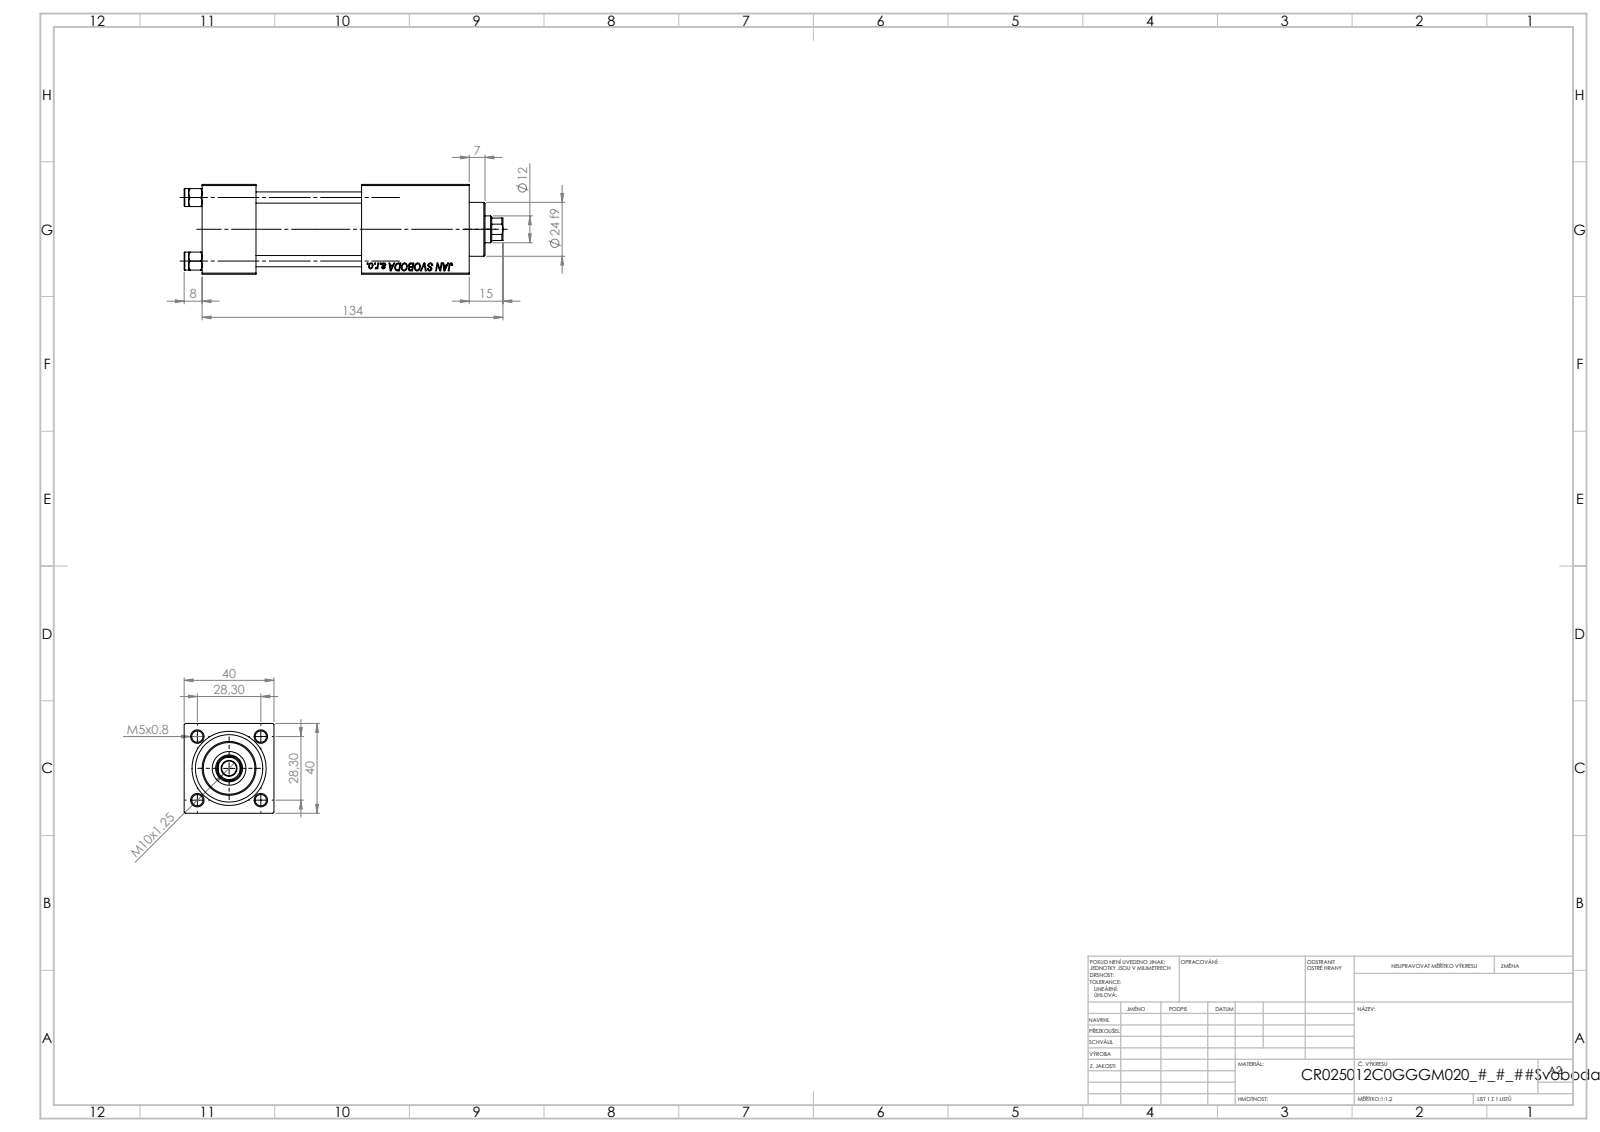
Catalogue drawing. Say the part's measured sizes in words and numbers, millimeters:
The part is named "NUT_M5_C; V215CR_C_Body; V215CR_C_TYCINKA; V215_VC_A (+1 more)". Its 3-D file was written by "SolidWorks 2019 (CONFIG_CONTROL_DESIGN)". It is 11 solids with 1148 faces: 525 planar, 87 cylindrical and 536 other. Overall it measures 142 by 40 by 40 millimeters. Its volume is 142 309 cubic millimeters and its surface area 54 443 square millimeters. Round holes: 4 of diameter 5, 3 of diameter 20, 2 of diameter 7, 2 of diameter 13.16, 1 of diameter 6.5, 1 of diameter 12, 1 of diameter 15, 1 of diameter 25, 1 of diameter 30. Round bosses or shafts: 4 of diameter 8, 1 of diameter 31, 1 of diameter 24. Partial cylindrical surfaces (rounded edges, fillets, slot ends): 1 of radius 5.5. The main face-to-face distances are 40, 24, 90.3, 66.3, 48, 71, 47, 19.3, 119, 95. The hole center spacings are 20.01, 28.3, 40.02, 72.
